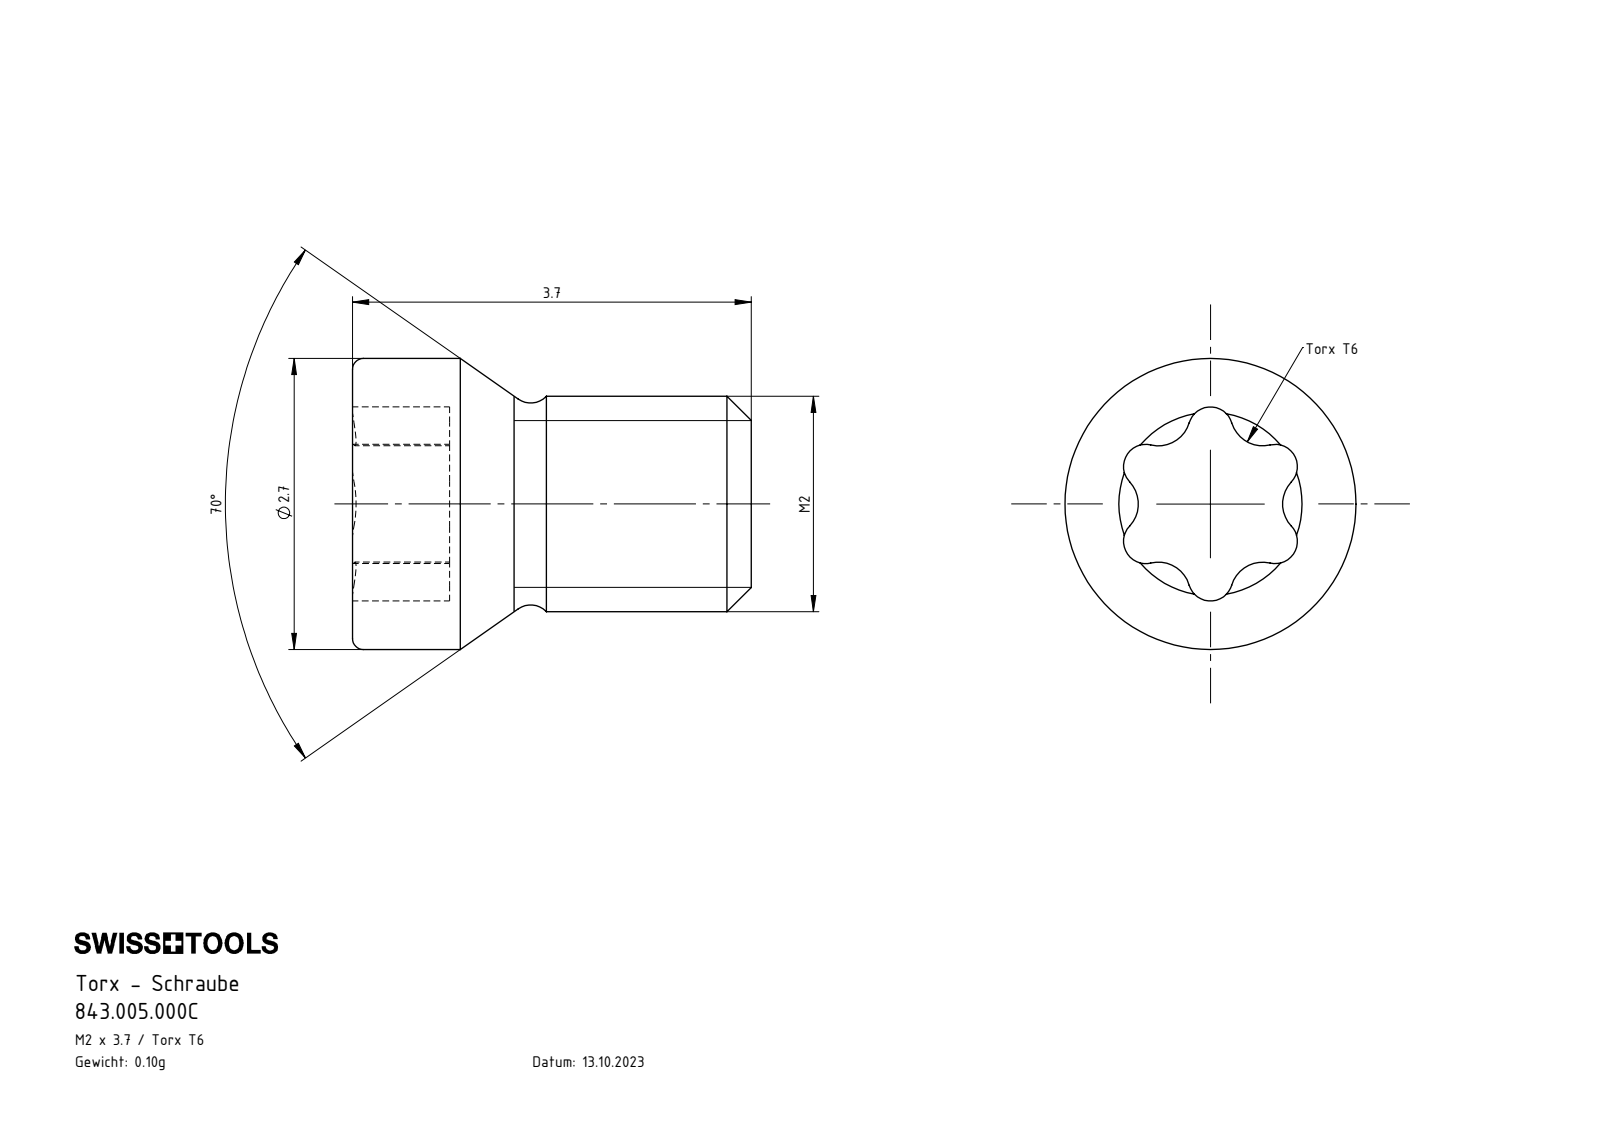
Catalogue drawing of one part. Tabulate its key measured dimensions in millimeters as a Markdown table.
| quantity | value |
| --- | --- |
| part name | 843.005.000C |
| STEP written by | SolidWorks 2022 (AUTOMOTIVE_DESIGN) |
| units | millimeters |
| bodies | 1 solid, 41 faces (3 planar, 19 cylindrical, 19 other) |
| overall size | 3.7 × 2.7 × 2.7 |
| volume | 13 mm³ |
| surface area | 40 mm² |
| round bosses / shafts (diameter × count) | 2.7 × 1, 2 × 1 |
| partial cylindrical surfaces (radius × count) | 0.21 × 6, 0.3 × 6 |
| main face-to-face distances | 0.9, 3.7, 2.8 |
